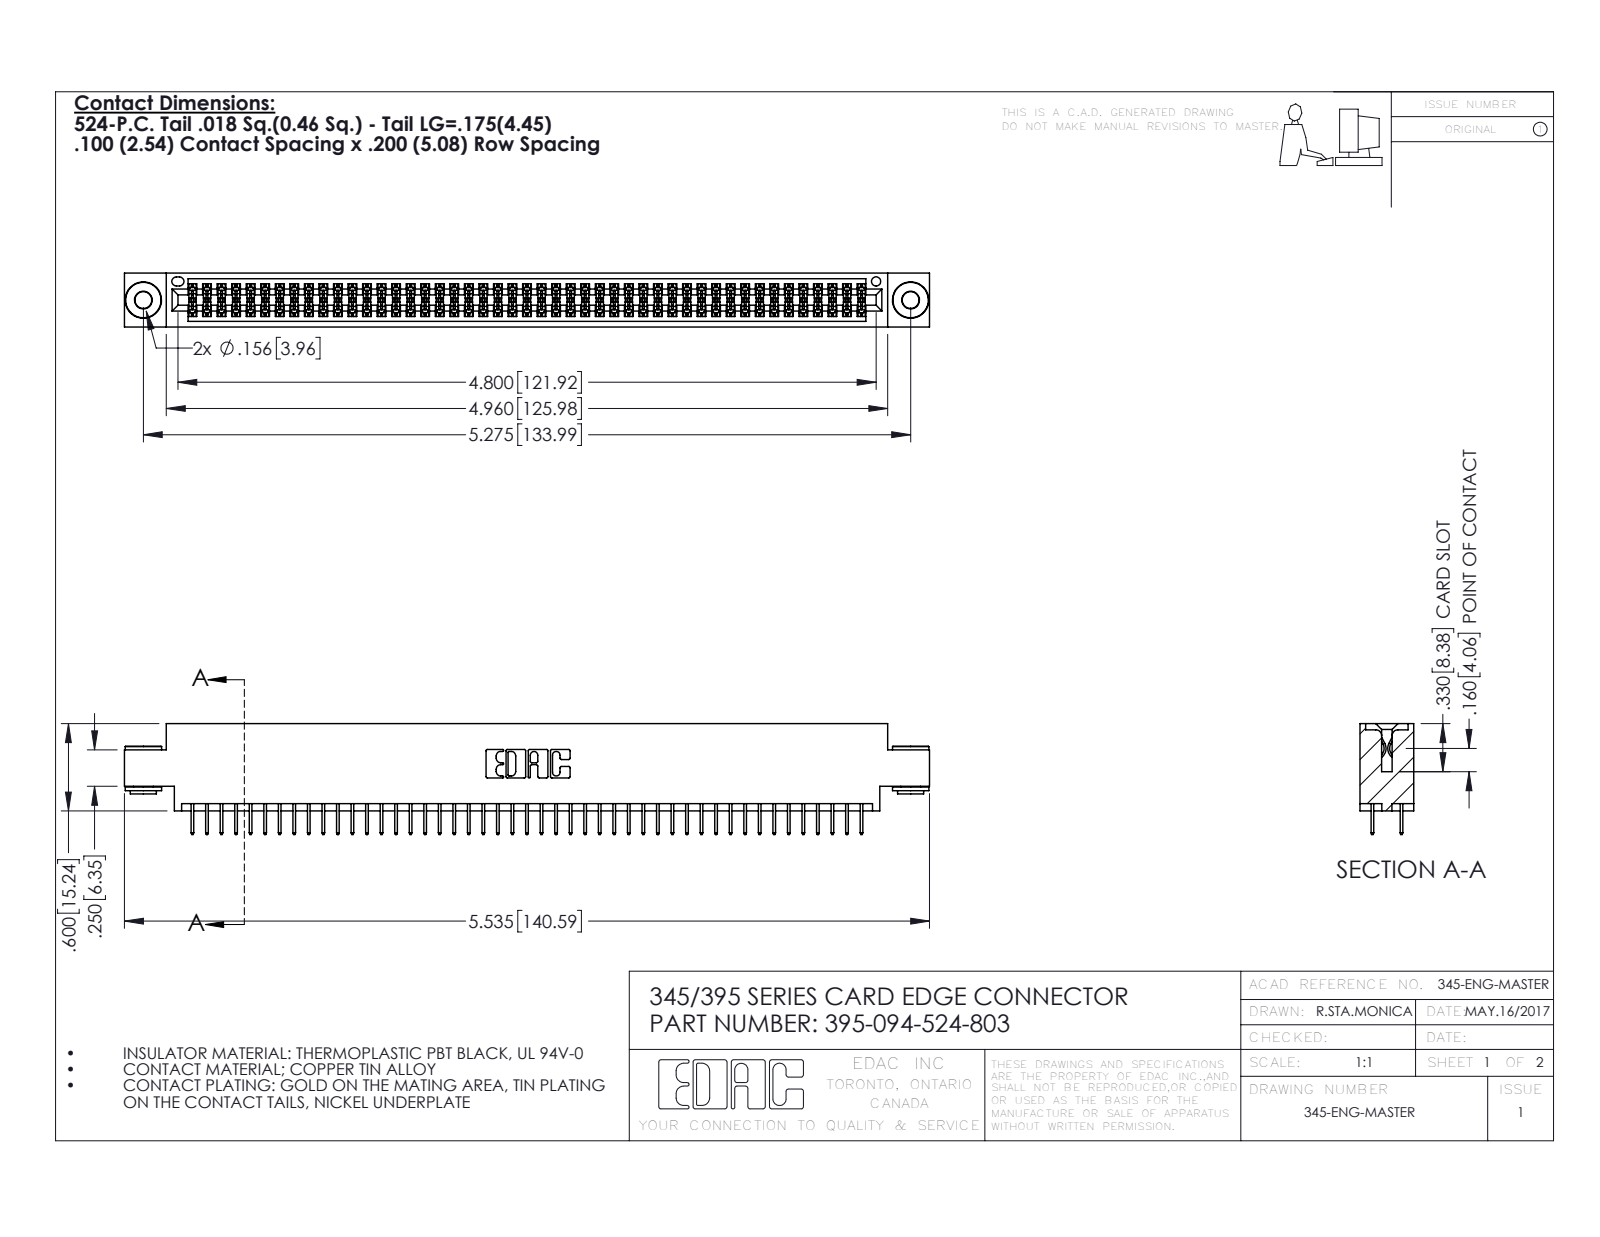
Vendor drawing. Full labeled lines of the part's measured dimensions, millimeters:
Part name (STEP PRODUCT): 345 Part_0.170 Offset - 0.156 Dia-TH; 395-094-524-803; 345-292-001_345-293-124; 345-250-002_345-250-002-102
STEP written by: SolidWorks 2016 (CONFIG_CONTROL_DESIGN)
Units: millimetres
Bodies: 97 solids, 5244 faces (3760 planar, 1476 cylindrical, 8 other)
Overall size (bounding box): 140.6 × 19.4 × 9.4
Volume: 13 500 mm³ · Surface area: 19 970 mm²
Round holes (diameter × count): ⌀2.9 ×2, ⌀4 ×2, ⌀1.6 ×1
Round bosses / shafts (diameter × count): ⌀6.4 ×2, ⌀4.6 ×2, ⌀3.5 ×2
Partial cylindrical surfaces — rounded edges, fillets, slot ends (radius × count): R0.2 ×141, R0.3 ×22, R0.2 ×6, R0.8 ×6, R0.7 ×3, R0.4 ×2, R0.5 ×2, R0.6 ×2
Main face-to-face distances: 1.8, 7.6, 9.4, 5.1, 2.5, 6.9, 0.6, 5.7, 4.4, 1.8
Hole centre spacings: 6.9, 128, 134
